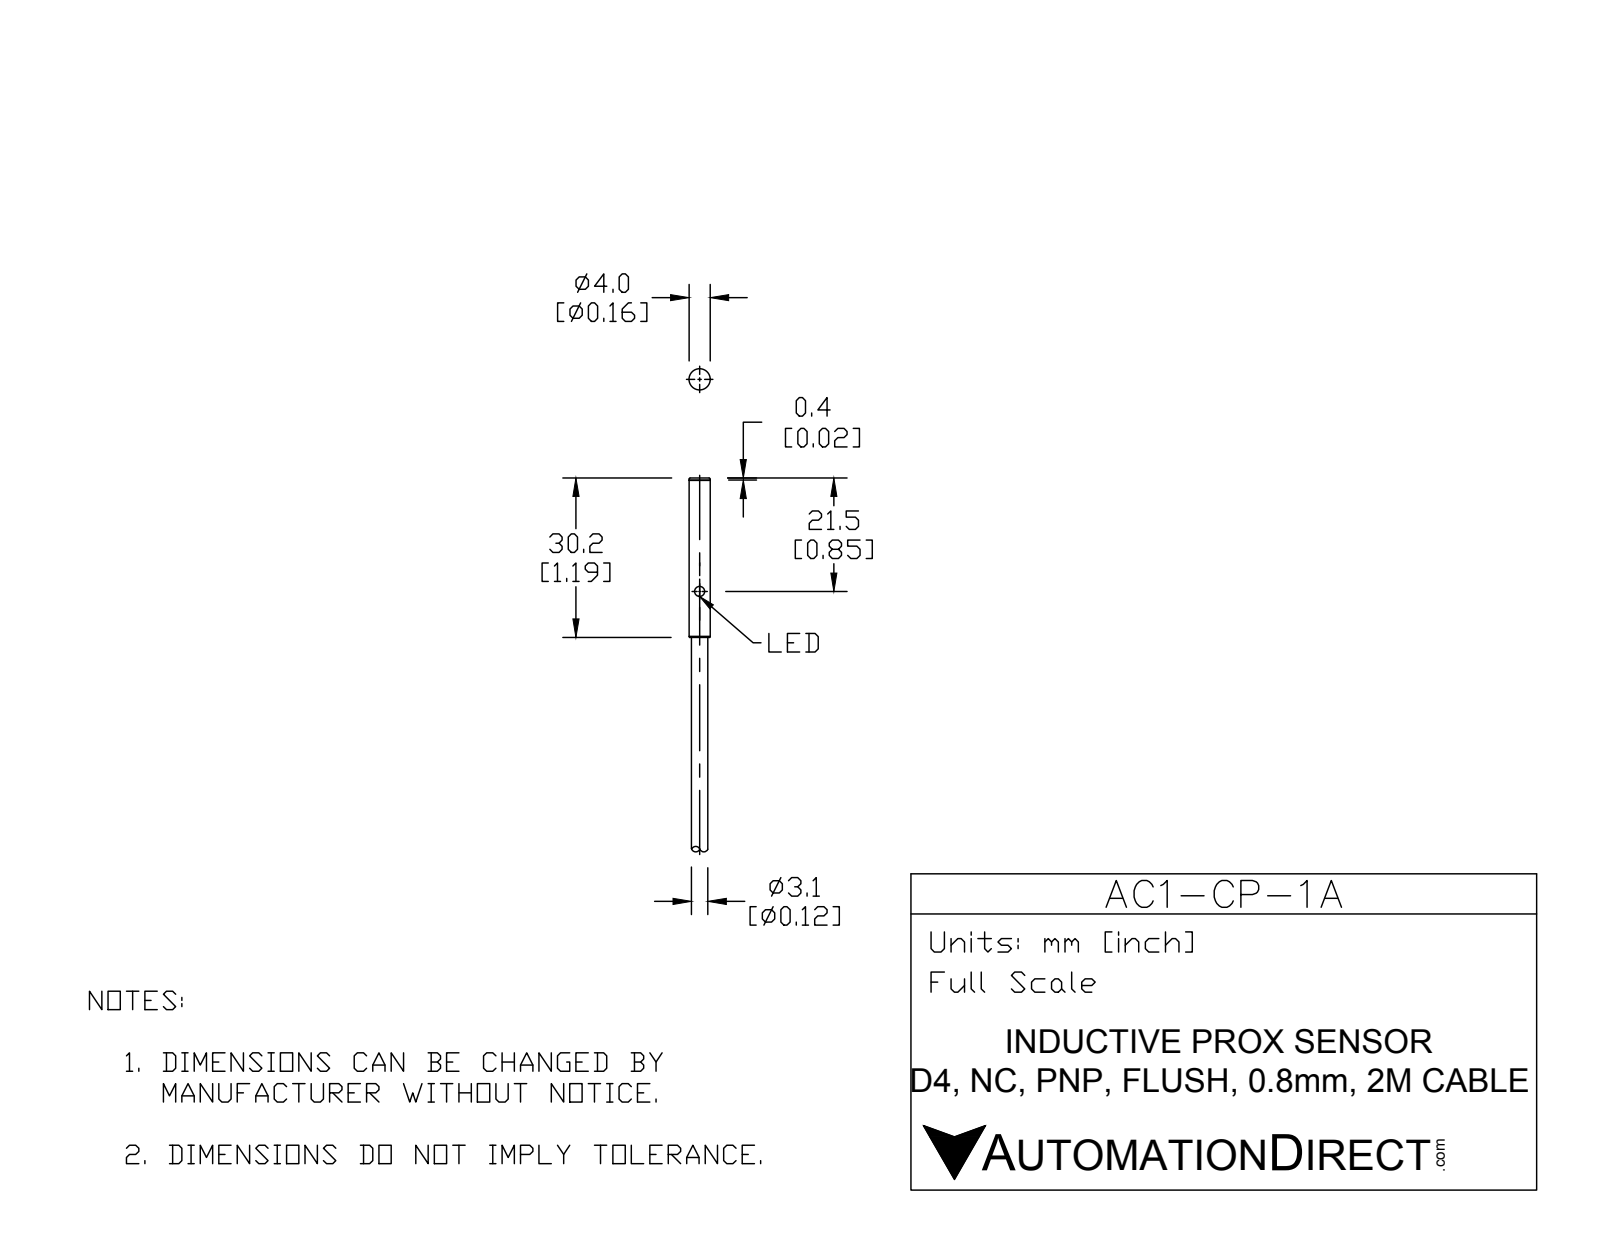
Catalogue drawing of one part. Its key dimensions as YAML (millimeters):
part_name: "AC1-CP-1A"
step_written_by: "SolidWorks 2015 (CONFIG_CONTROL_DESIGN)"
units: millimeters
bodies: {solids: 2, faces: 20, planar: 6, cylindrical: 8, other: 6}
overall_size: [80.2, 4, 4]
volume: 756
surface_area: 905
round_holes:
  - {diameter: 1.9, count: 1}
round_bosses_or_shafts:
  - {diameter: 4, count: 1}
  - {diameter: 3.1, count: 1}
face_to_face_distances: [30.2, 50, 80.2, 79.8, 29.8, 0.4]
